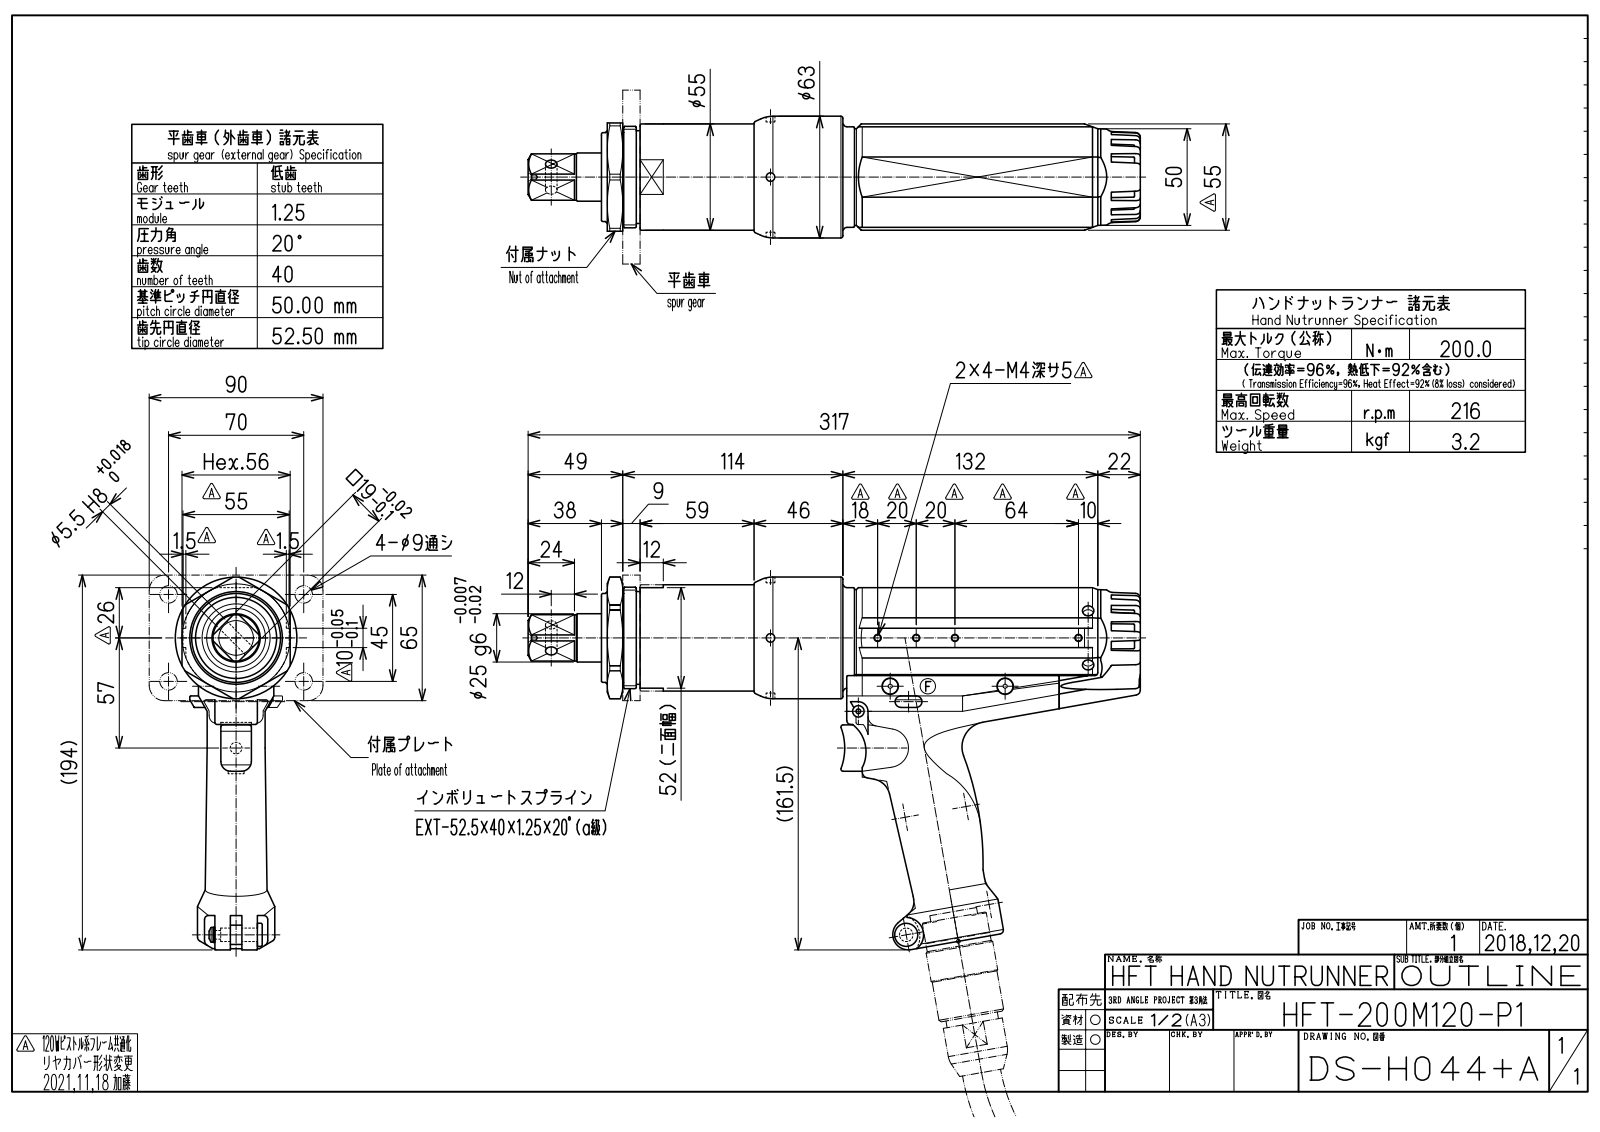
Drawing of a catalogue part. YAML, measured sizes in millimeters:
part_name: "HFT-200M120-P1(DS-H044+B)_OUTLINE"
step_written_by: "Autodesk Inventor 2023 (CONFIG_CONTROL_DESIGN)"
units: millimeters
bodies: {solids: 1, faces: 1798, planar: 758, cylindrical: 392, other: 648}
overall_size: [317, 192.96, 63]
volume: 871390
surface_area: 126801
round_holes:
  - {diameter: 6, count: 6}
  - {diameter: 3.24, count: 5}
  - {diameter: 3.3, count: 4}
  - {diameter: 4.6, count: 4}
  - {diameter: 1.6, count: 3}
  - {diameter: 1.3, count: 2}
  - {diameter: 2.46, count: 2}
  - {diameter: 8.5, count: 2}
  - {diameter: 2.5, count: 1}
  - {diameter: 3.5, count: 1}
  - {diameter: 4.5, count: 1}
  - {diameter: 5.5, count: 1}
round_bosses_or_shafts:
  - {diameter: 1, count: 24}
  - {diameter: 5.5, count: 5}
  - {diameter: 1.6, count: 4}
  - {diameter: 5.8, count: 3}
  - {diameter: 30, count: 2}
  - {diameter: 8, count: 2}
  - {diameter: 63, count: 1}
  - {diameter: 60, count: 1}
partial_cylinders:
  - {radius: 0.5, count: 20}
  - {radius: 1, count: 18}
  - {radius: 0.3, count: 7}
  - {radius: 2, count: 5}
  - {radius: 5, count: 4}
  - {radius: 1.5, count: 3}
  - {radius: 2.5, count: 3}
  - {radius: 3, count: 3}
face_to_face_distances: [1.5, 6.5, 35.5, 10, 53.5, 8.5, 8, 45.5, 0.5, 7]
hole_center_spacings: [20, 19, 11.08, 13.02, 13.97, 14.54, 15.38, 18.18]
